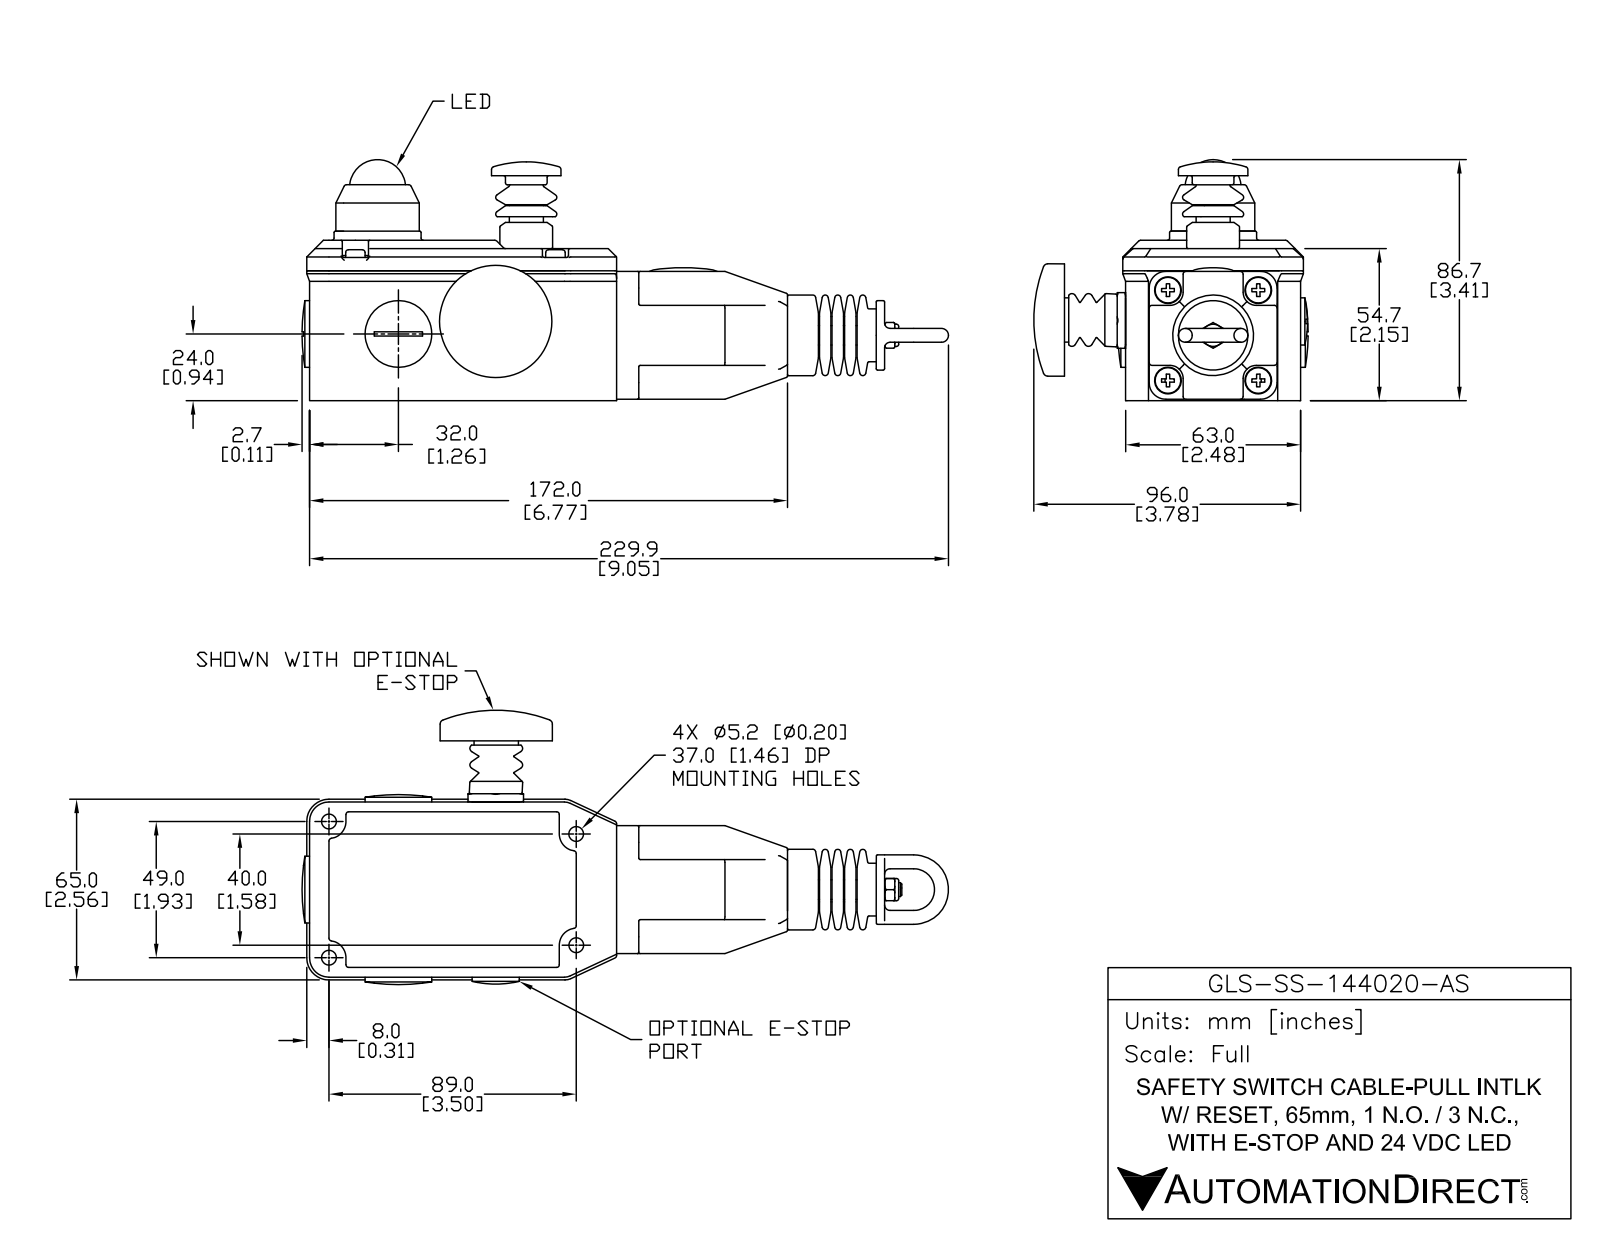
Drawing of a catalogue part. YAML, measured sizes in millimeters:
part_name: "GLS-SS-144020-AS"
step_written_by: "SolidWorks 2013 (AUTOMOTIVE_DESIGN)"
units: millimeters
bodies: {solids: 2, faces: 685, planar: 204, cylindrical: 236, other: 245}
overall_size: [233.8, 104.37, 86]
volume: 527351
surface_area: 65123
round_holes:
  - {diameter: 5.2, count: 4}
  - {diameter: 9.5, count: 4}
  - {diameter: 21, count: 1}
round_bosses_or_shafts:
  - {diameter: 9.2, count: 4}
  - {diameter: 6, count: 4}
  - {diameter: 26.8, count: 2}
  - {diameter: 25, count: 2}
  - {diameter: 19, count: 2}
  - {diameter: 5, count: 2}
  - {diameter: 40, count: 1}
  - {diameter: 31.3, count: 1}
partial_cylinders:
  - {radius: 0.5, count: 74}
  - {radius: 0.75, count: 20}
  - {radius: 1, count: 8}
  - {radius: 3, count: 4}
  - {radius: 4.5, count: 4}
  - {radius: 4.8, count: 4}
  - {radius: 5, count: 4}
  - {radius: 16, count: 4}
face_to_face_distances: [54.4, 65, 54.7, 11.7, 33.3, 45, 90.65, 25.65, 4.5, 9.98]
hole_center_spacings: [32.5, 32.6, 46.03, 89.11, 99.51, 28.87, 29.27, 40]
